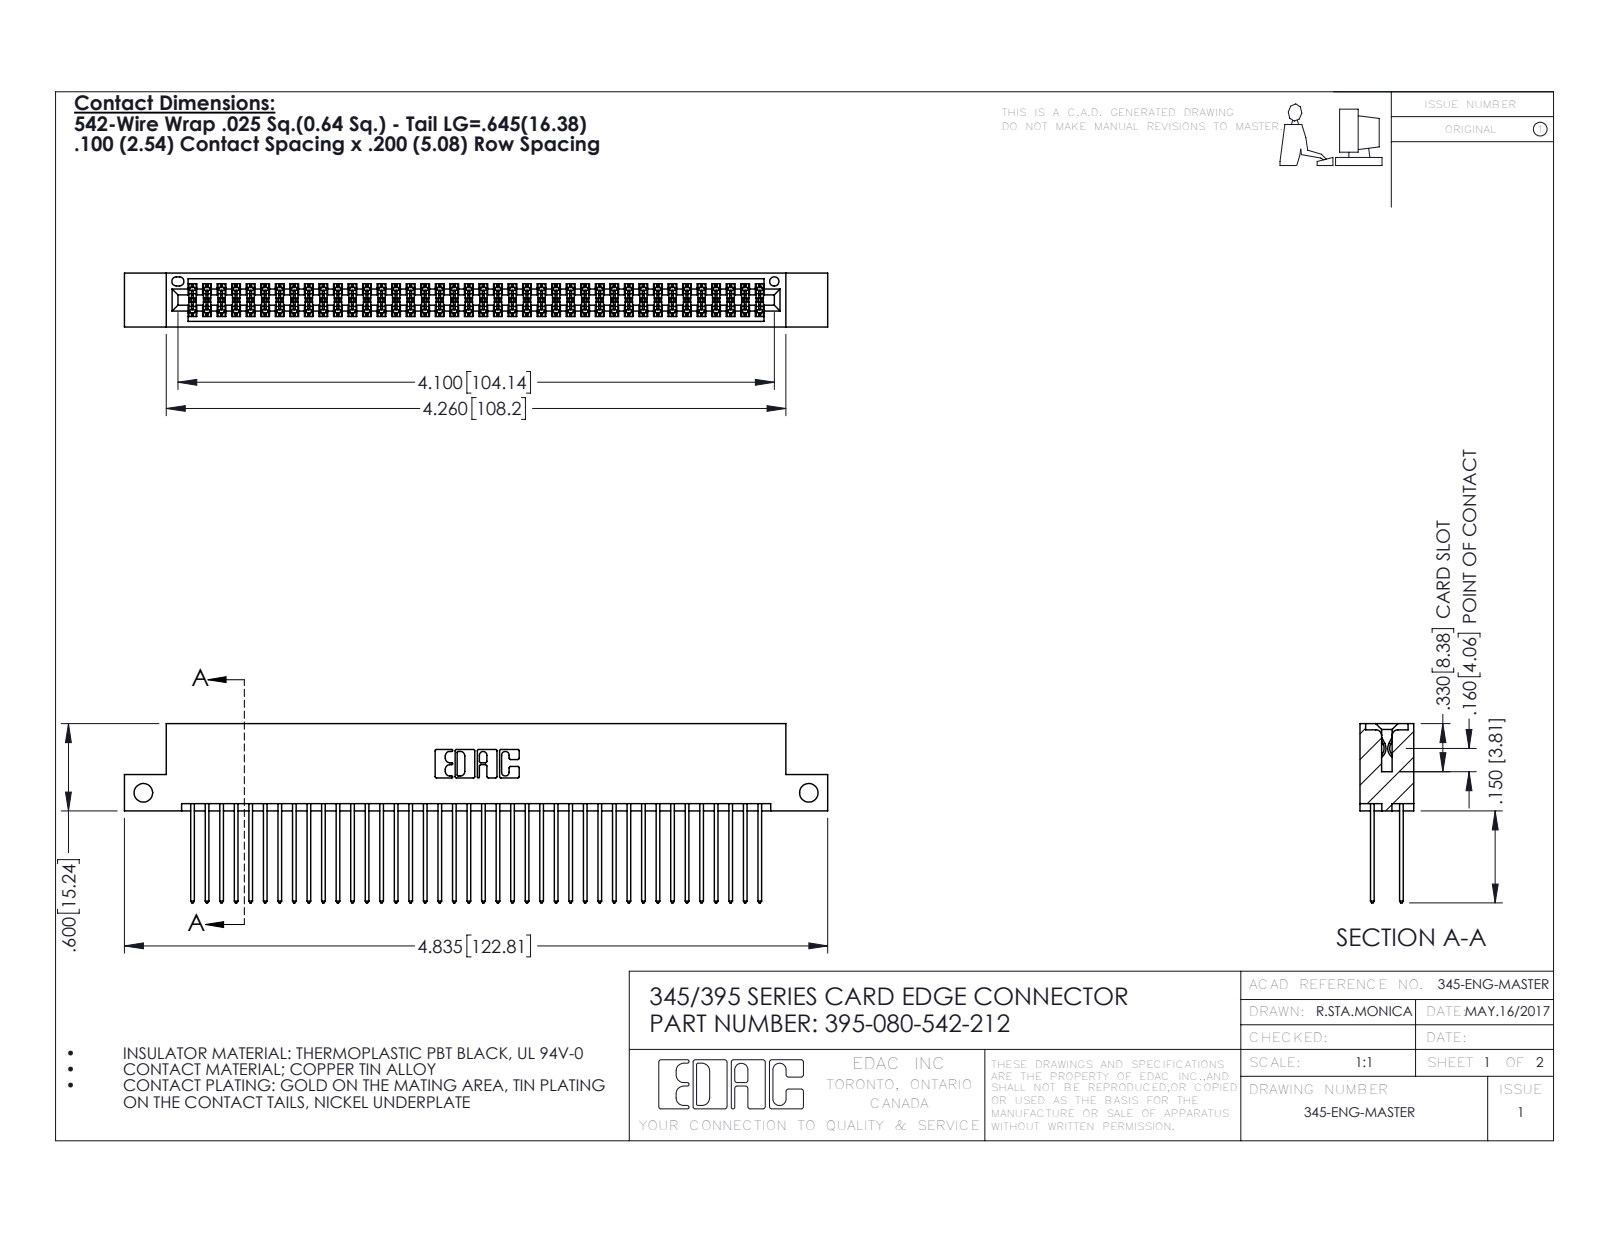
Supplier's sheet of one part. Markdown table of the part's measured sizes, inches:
| quantity | value |
| --- | --- |
| part name | 345-292-001_345-293-142; 395-080-542-212; 345 Part_Flush Mounting Lugs - Side Mount |
| STEP written by | SolidWorks 2016 (CONFIG_CONTROL_DESIGN) |
| units | inches |
| bodies | 81 solids, 4126 faces (2720 planar, 1406 cylindrical, 0 other) |
| overall size | 4.835 × 1.232 × 0.37 |
| volume | 0.744 in³ |
| surface area | 30.38 in² |
| round holes (diameter × count) | 0.128 × 2, 0.064 × 1 |
| partial cylindrical surfaces (radius × count) | 0.006 × 120, 0.01 × 80, 0.01 × 22, 0.007 × 6, 0.031 × 6, 0.026 × 3, 0.014 × 2, 0.019 × 2 |
| main face-to-face distances | 0.298, 0.072, 0.2, 0.098, 0.272, 0.025, 0.225, 0.37, 0.175, 0.149 |
| hole center spacings | 4.575 |
